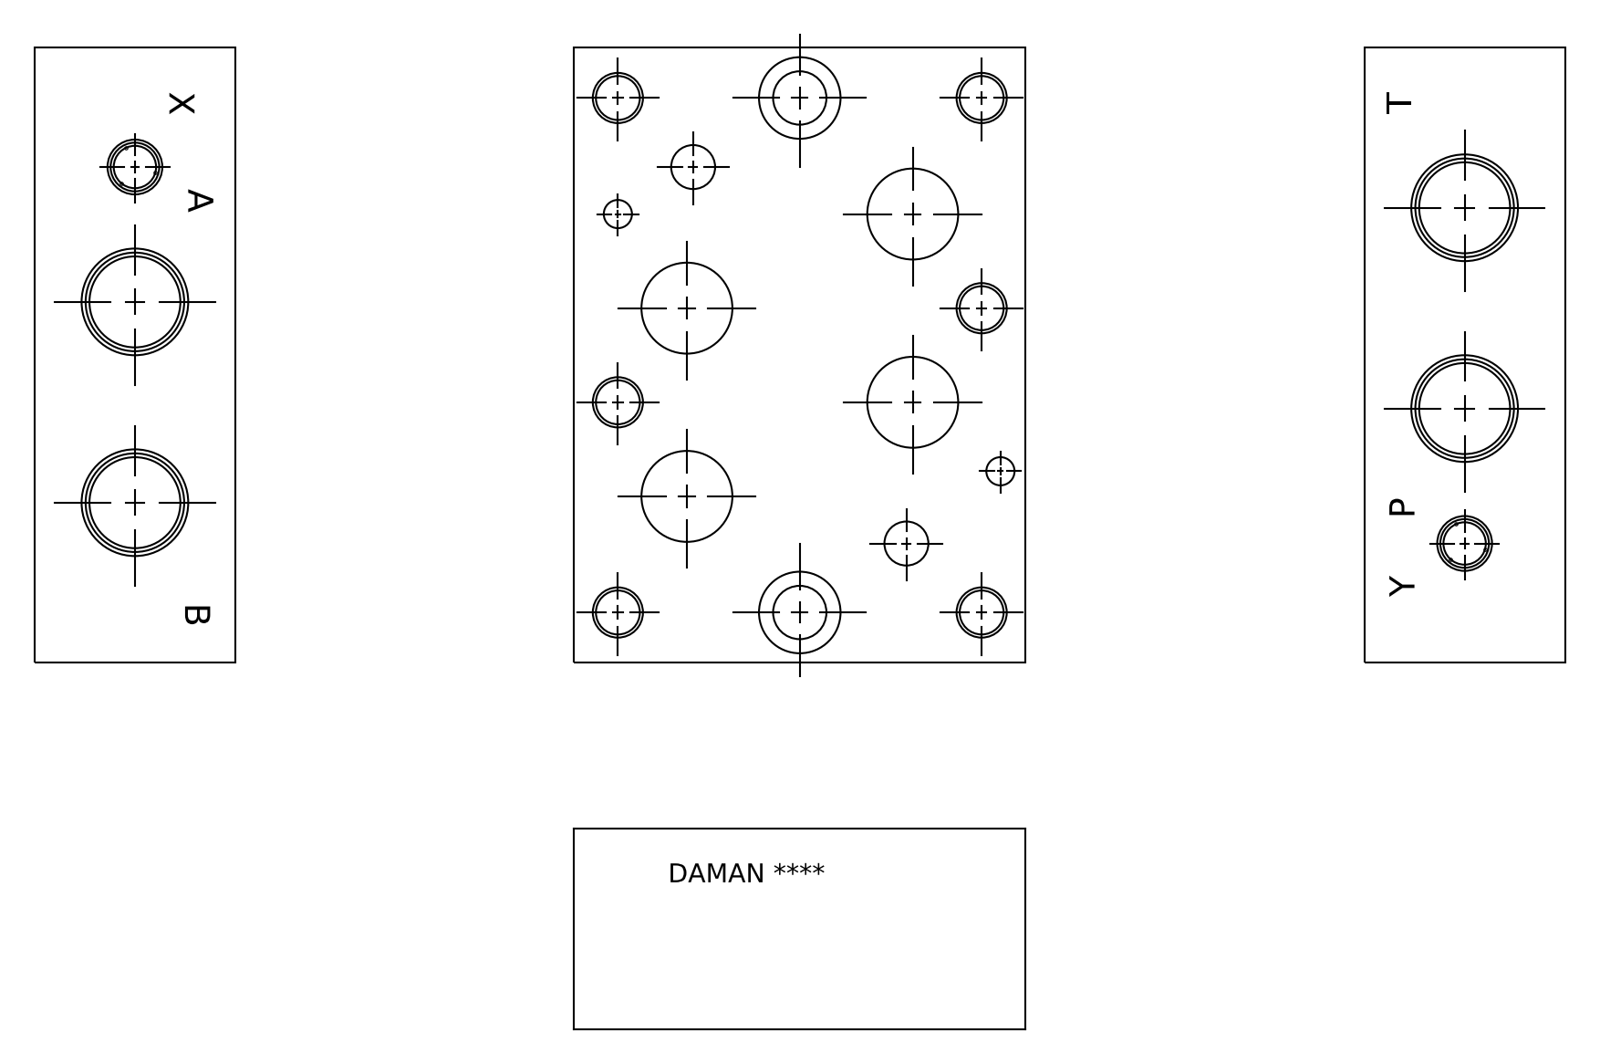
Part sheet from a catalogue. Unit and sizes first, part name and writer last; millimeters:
Units: millimetres
Overall size (bounding box): 155.57 × 114.3 × 50.8
Round holes (diameter × count): ⌀10.72 ×8, ⌀23.01 ×8, ⌀12.7 ×6, ⌀26.92 ×4, ⌀7.14 ×2, ⌀11.89 ×2, ⌀13.49 ×2, ⌀13.87 ×2, ⌀20.62 ×2
Main face-to-face distances: 50.8, 114.3, 155.57, 25.4, 15.85, 98.45, 82.6, 6.35, 19.05, 31.75
Hole centre spacings: 46.04, 29.52, 29.54, 32.15, 35.75, 40.97, 47.62, 53.18
Volume: 790 388 mm³ · Surface area: 86 951 mm²
Bodies: 1 solid, 506 faces (307 planar, 36 cylindrical, 163 other)
Part name (STEP PRODUCT): Part_AD08SPSO12P_3D
STEP written by: Autodesk Inventor 2019 (AUTOMOTIVE_DESIGN)
